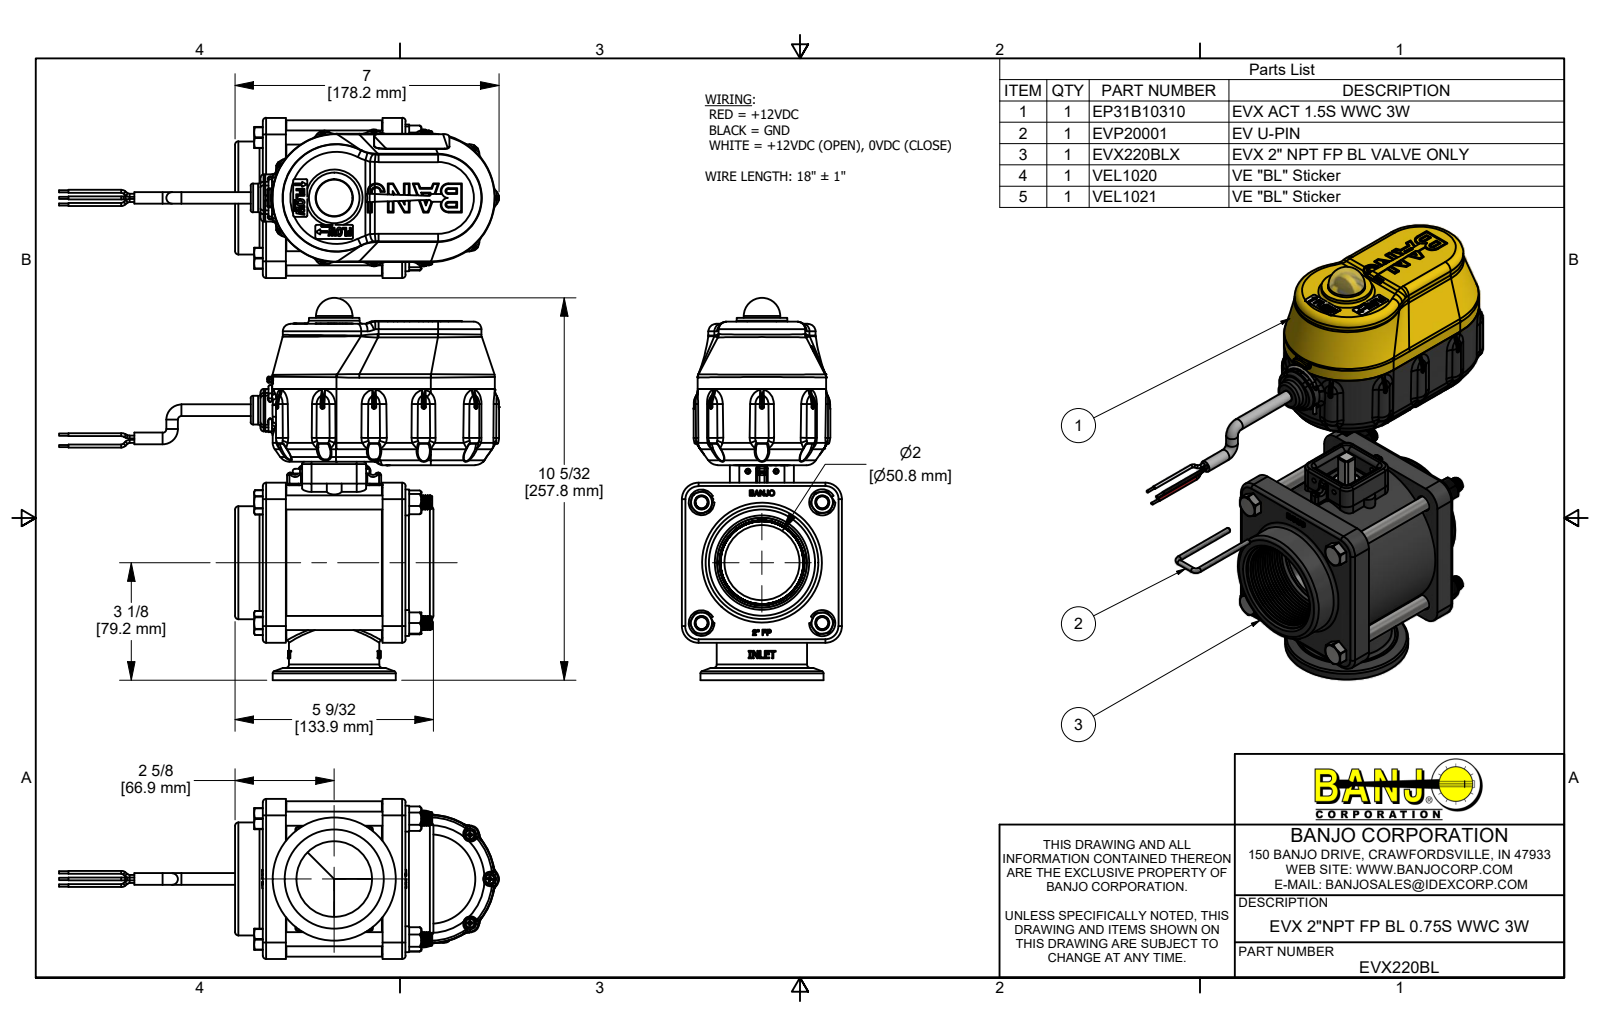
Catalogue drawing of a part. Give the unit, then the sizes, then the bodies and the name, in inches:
Units: inches
Overall size (bounding box): 11.685 × 10.15 × 4.25
Round holes (diameter × count): ⌀0.095 ×11, ⌀0.15 ×11, ⌀0.08 ×7, ⌀0.107 ×4, ⌀0.126 ×4, ⌀0.136 ×4, ⌀0.148 ×4, ⌀0.15 ×4, ⌀0.17 ×4, ⌀0.307 ×4, ⌀0.385 ×4, ⌀0.438 ×4
Round bosses / shafts (diameter × count): ⌀0.324 ×60, ⌀0.25 ×17, ⌀0.08 ×15, ⌀0.14 ×11, ⌀0.108 ×11, ⌀0.085 ×11, ⌀0.058 ×6, ⌀0.375 ×5
Partial cylindrical surfaces — rounded edges, fillets, slot ends (radius × count): R0.013 ×180, R0.04 ×145, R0.01 ×84, R0.02 ×74, R0.005 ×53, R0.03 ×38, R0.06 ×28, R0.08 ×28
Main face-to-face distances: 0.1, 2.565, 0.61, 3.18, 3.79, 2.485, 0.695, 3.095, 0.085, 0.211
Hole centre spacings: 2.265, 2.69, 2.715, 3.204, 1.662, 1.774, 2.458, 2.73
Volume: 76.23 in³ · Surface area: 761 in²
Bodies: 98 solids, 11962 faces (3409 planar, 3348 cylindrical, 5205 other)
Part name (STEP PRODUCT): EVX220BL; EP31B10310; B61905PPHS; B632038PM (+8 more)
STEP written by: Autodesk Inventor 2019 (AUTOMOTIVE_DESIGN)
